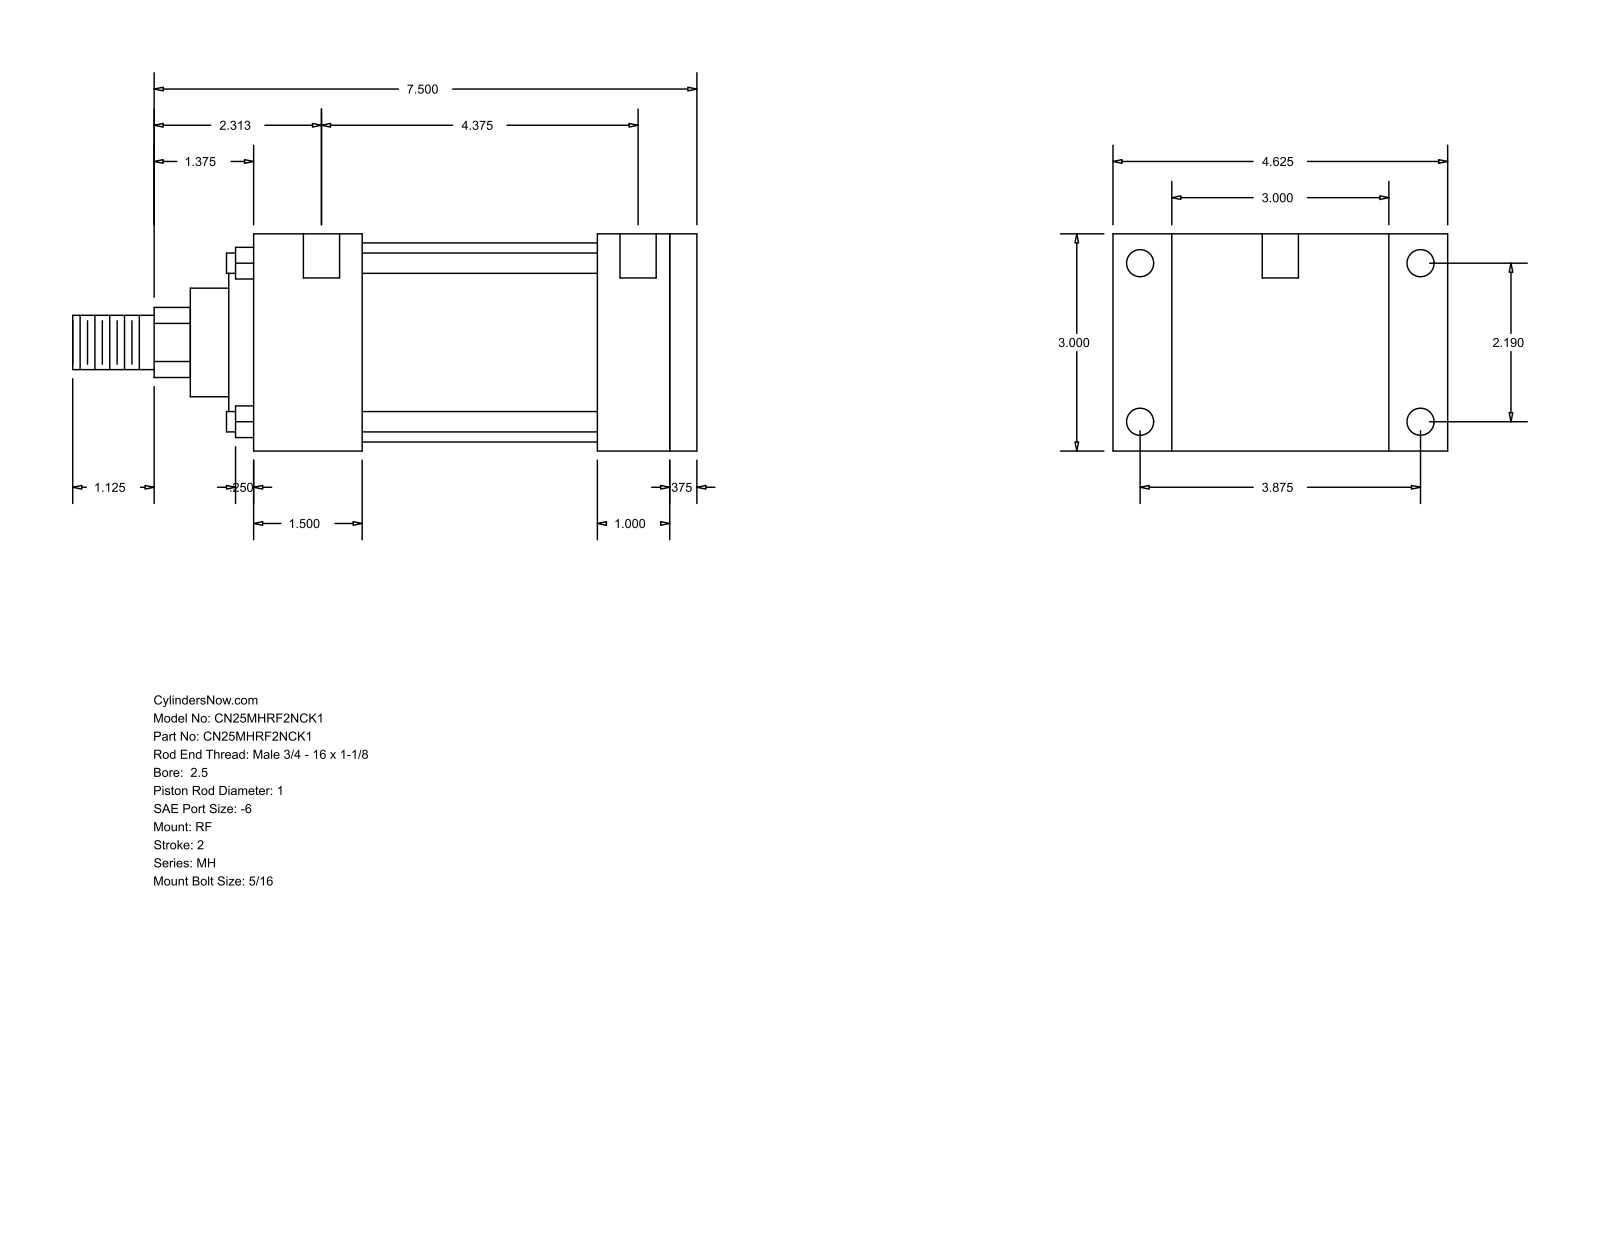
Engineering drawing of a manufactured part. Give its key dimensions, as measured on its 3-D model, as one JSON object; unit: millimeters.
{"part_name": "MH_RF__0250_1", "step_written_by": "GSSL Pune (CONFIG_CONTROL_DESIGN)", "units": "millimeters", "bodies": {"solids": 0, "faces": 94, "planar": 65, "cylindrical": 29, "other": 0}, "overall_size": [219.07, 117.47, 76.2], "round_holes": [[5.56, 4], [9.53, 4], [12.7, 2]], "round_bosses_or_shafts": [[7.14, 4], [69.85, 1], [60.33, 1], [38.1, 1], [25.4, 1], [19.05, 1]], "partial_cylinders_radius": [[12.29, 1]], "face_to_face_distances": [76.2, 9.53, 146.05, 155.58, 25.4, 120.65, 34.93, 38.11, 82.54, 107.94], "hole_center_spacings": [55.62, 98.42, 113.05, 119.06, 3.18, 4.76, 111.12, 114.3]}
